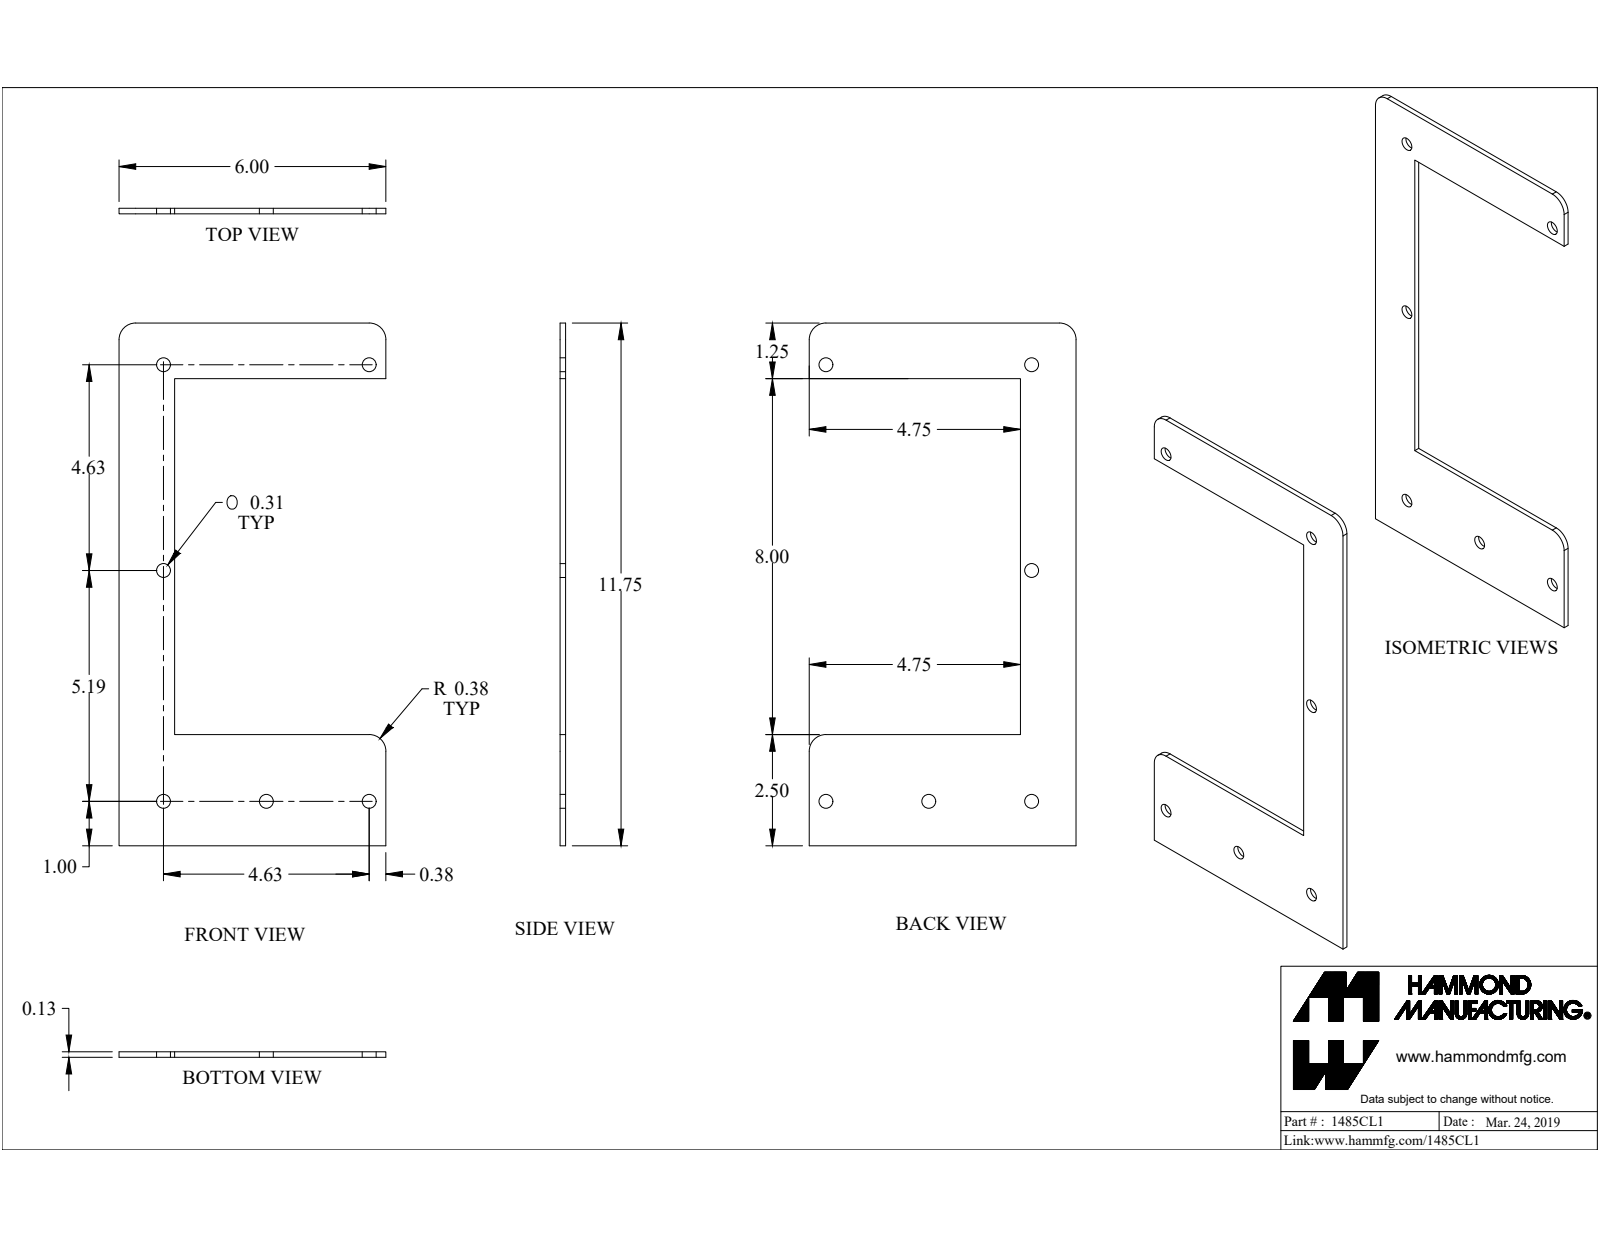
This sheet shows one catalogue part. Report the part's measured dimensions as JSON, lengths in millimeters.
{"part_name": "1485CL1", "step_written_by": "SolidWorks 2019 (CONFIG_CONTROL_DESIGN)", "units": "millimeters", "bodies": {"solids": 1, "faces": 19, "planar": 10, "cylindrical": 9, "other": 0}, "overall_size": [298.5, 152.4, 3.2], "volume_mm3": 65450, "surface_area_mm2": 45290, "round_holes": [[8, 6]], "partial_cylinders_radius": [[9.5, 3]], "face_to_face_distances": [3.2, 31.8, 298.5, 266.7, 235, 203.2, 63.5, 152.4, 120.7], "hole_center_spacings": [117.5, 58.8, 249.3, 256.1, 275.5, 131.7, 144.3, 166.1]}
